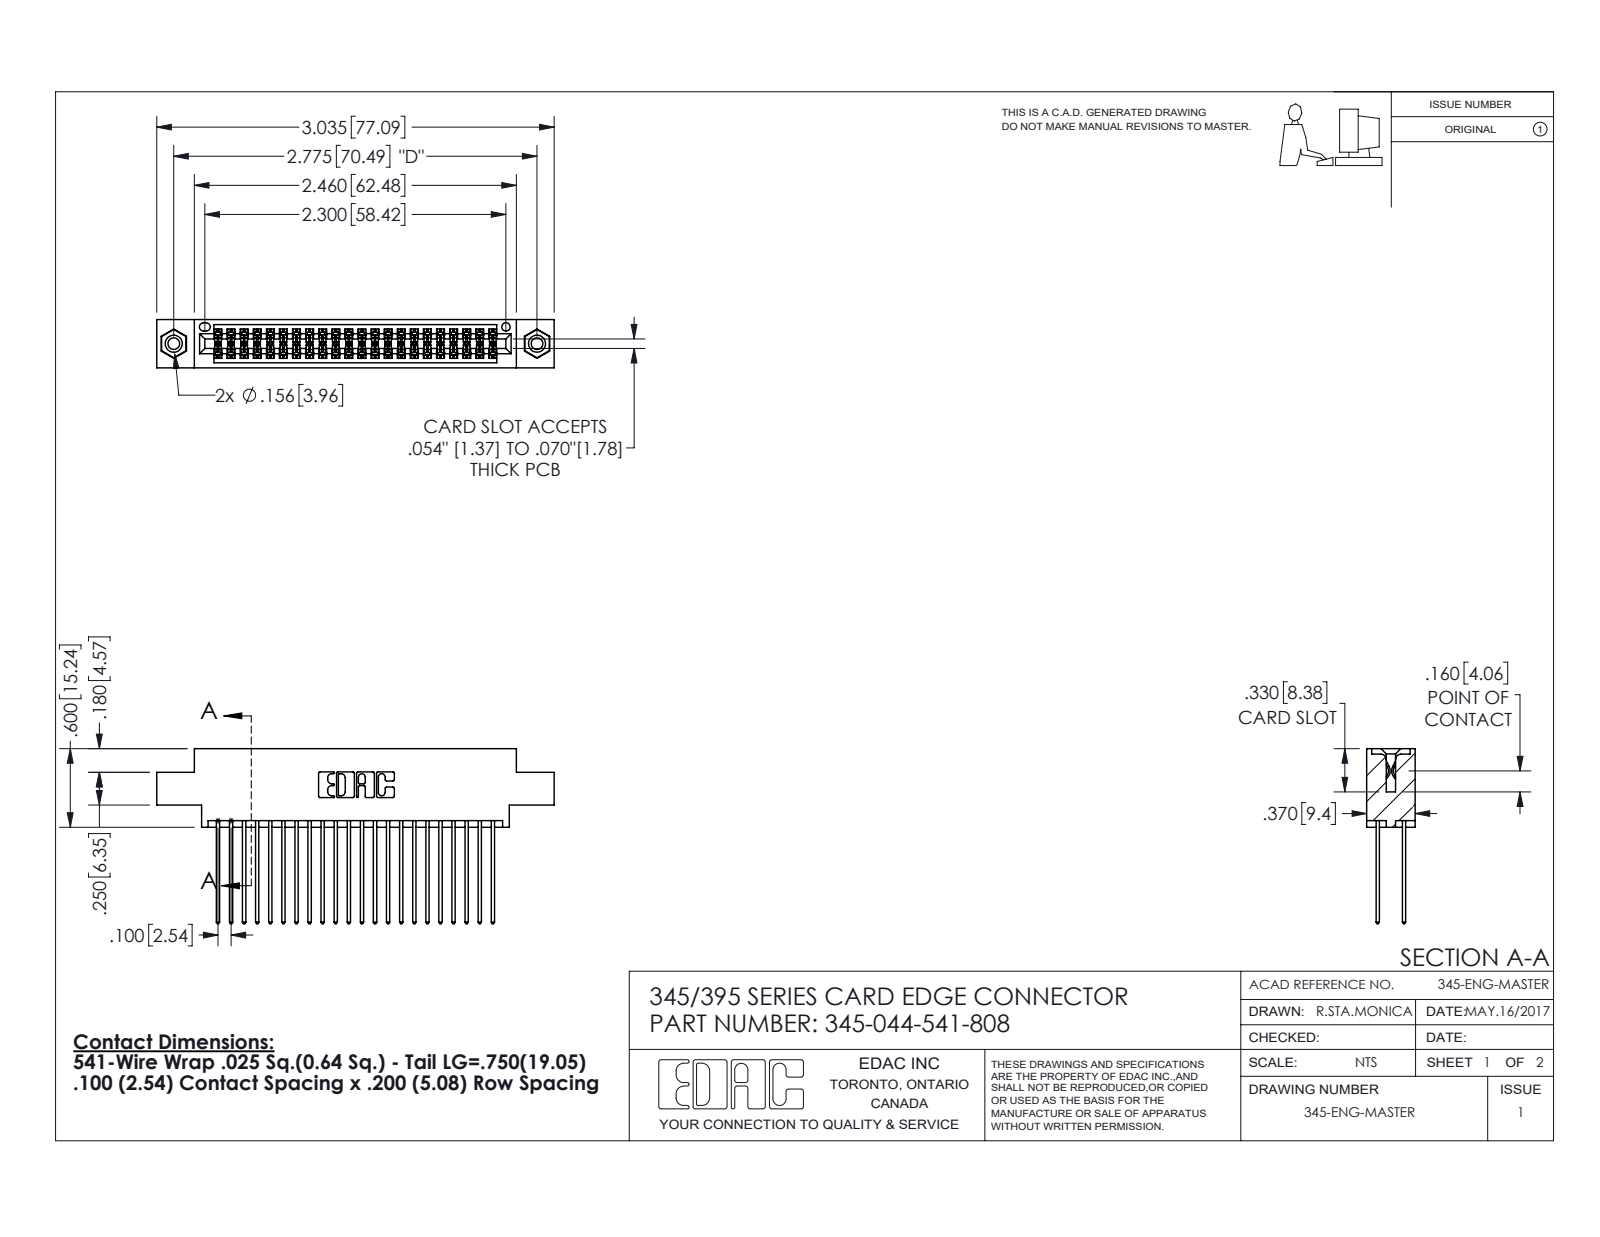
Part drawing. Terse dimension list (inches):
name: 345-044-541-808; 345 Part_0.170 Offset - 0.156 Dia-TI; 345-292-001_345-293-141; 345-250-001_345-250-003-102
written by: SolidWorks 2016 (CONFIG_CONTROL_DESIGN)
unit: in
bodies: 47 solids, 2390 faces (1568 planar, 806 cylindrical, 16 other)
size: 3.035 × 1.337 × 0.37
volume: 0.454 in³; area: 18.52 in²
holes: 2× ⌀0.089, 2× ⌀0.125, 2× ⌀0.156, 1× ⌀0.064
bosses: 2× ⌀0.155
rounds: 66× R0.006, 44× R0.01, 22× R0.01, 6× R0.007, 6× R0.031, 3× R0.026, 2× R0.014, 2× R0.019
face distances: 0.072, 0.298, 0.2, 0.098, 0.272, 0.025, 0.37, 0.225, 0.175, 0.149
hole spacings: 0.27, 2.541, 2.775
